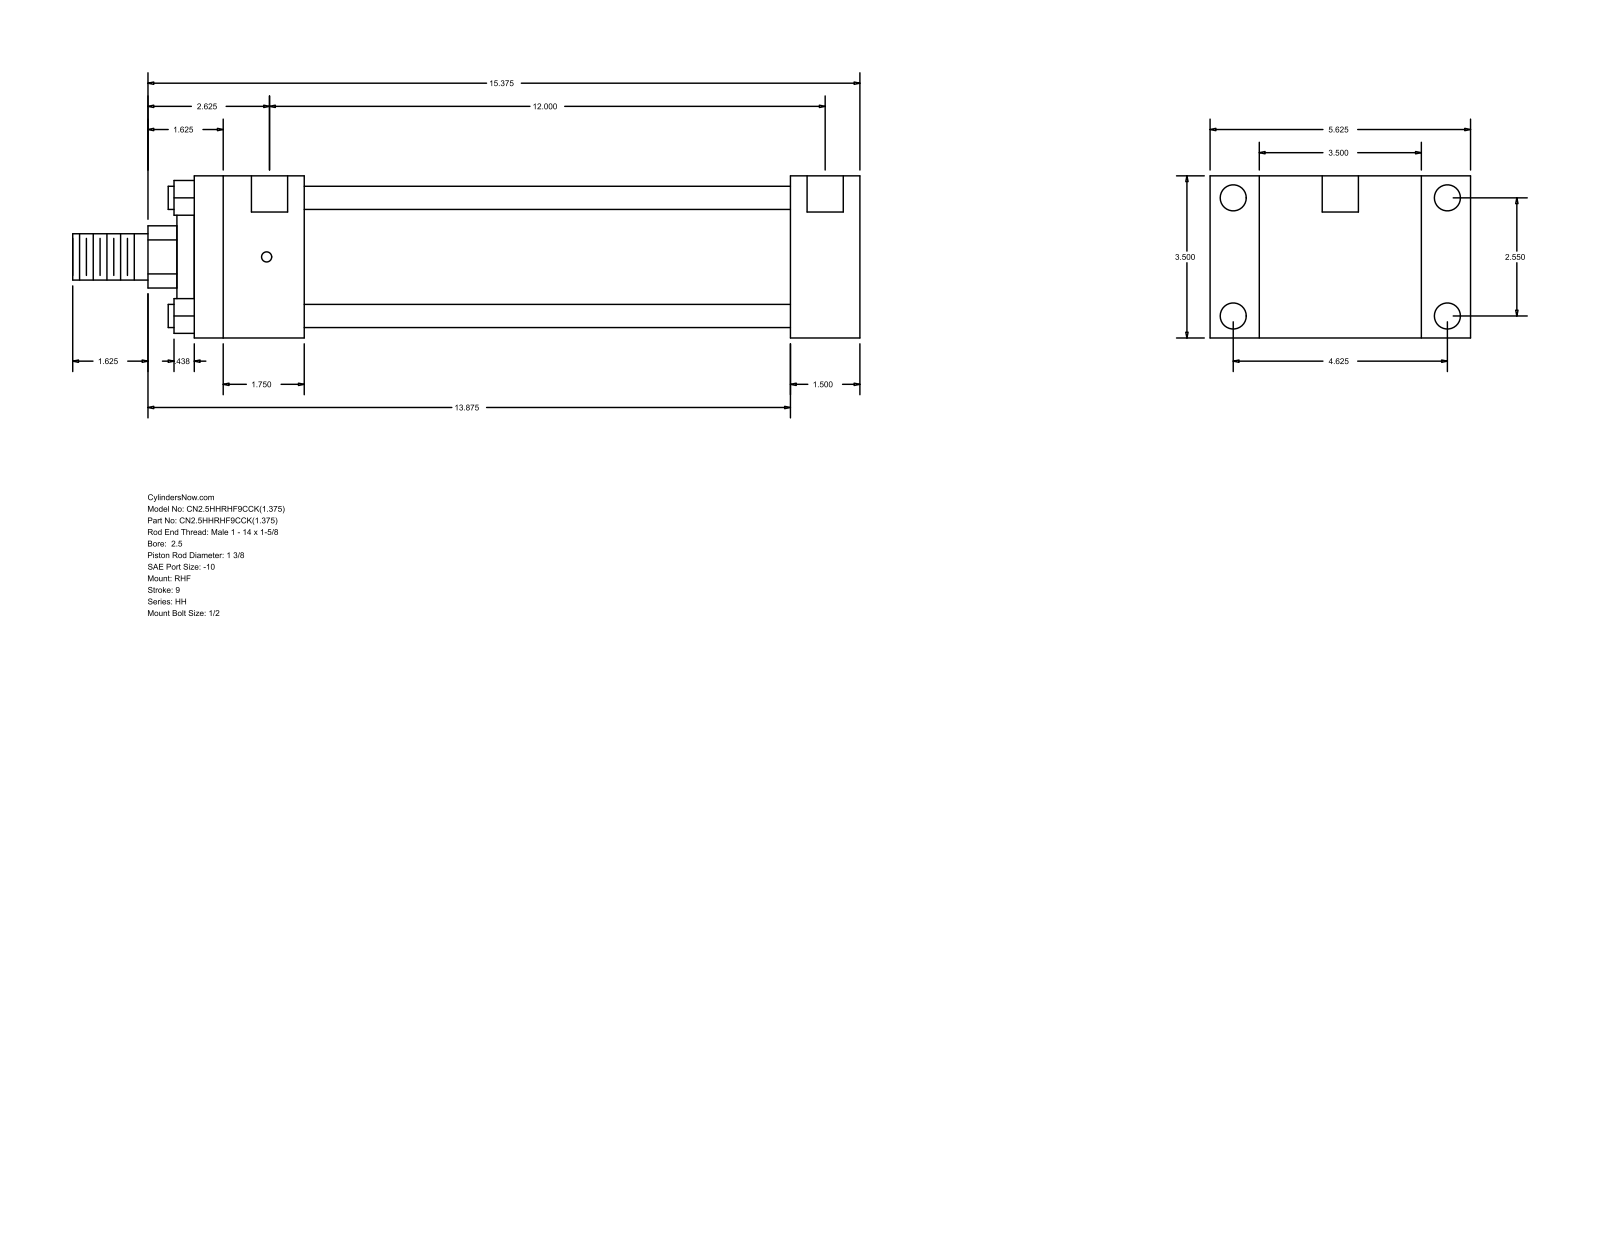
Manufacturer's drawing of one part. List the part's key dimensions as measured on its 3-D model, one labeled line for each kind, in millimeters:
Part name (STEP PRODUCT): HH_RHF__0250_1.375
STEP written by: GSSL Pune (CONFIG_CONTROL_DESIGN)
Units: millimetres
Bodies: 0 solids, 88 faces (60 planar, 28 cylindrical, 0 other)
Overall size (bounding box): 431.8 × 142.88 × 88.9
Round holes (diameter × count): ⌀5.56 ×4, ⌀14.3 ×4, ⌀19.84 ×2
Round bosses / shafts (diameter × count): ⌀12.7 ×4, ⌀73.03 ×1, ⌀50.8 ×1, ⌀34.92 ×1, ⌀25.4 ×1
Partial cylindrical surfaces — rounded edges, fillets, slot ends (radius × count): R17.06 ×1
Main face-to-face distances: 88.9, 38.09, 26.99, 115.89, 327.03, 365.12, 142.88, 60.32, 266.71, 304.8
Hole centre spacings: 1.58, 64.76, 117.48, 134.15, 306.39, 307.97, 304.81
